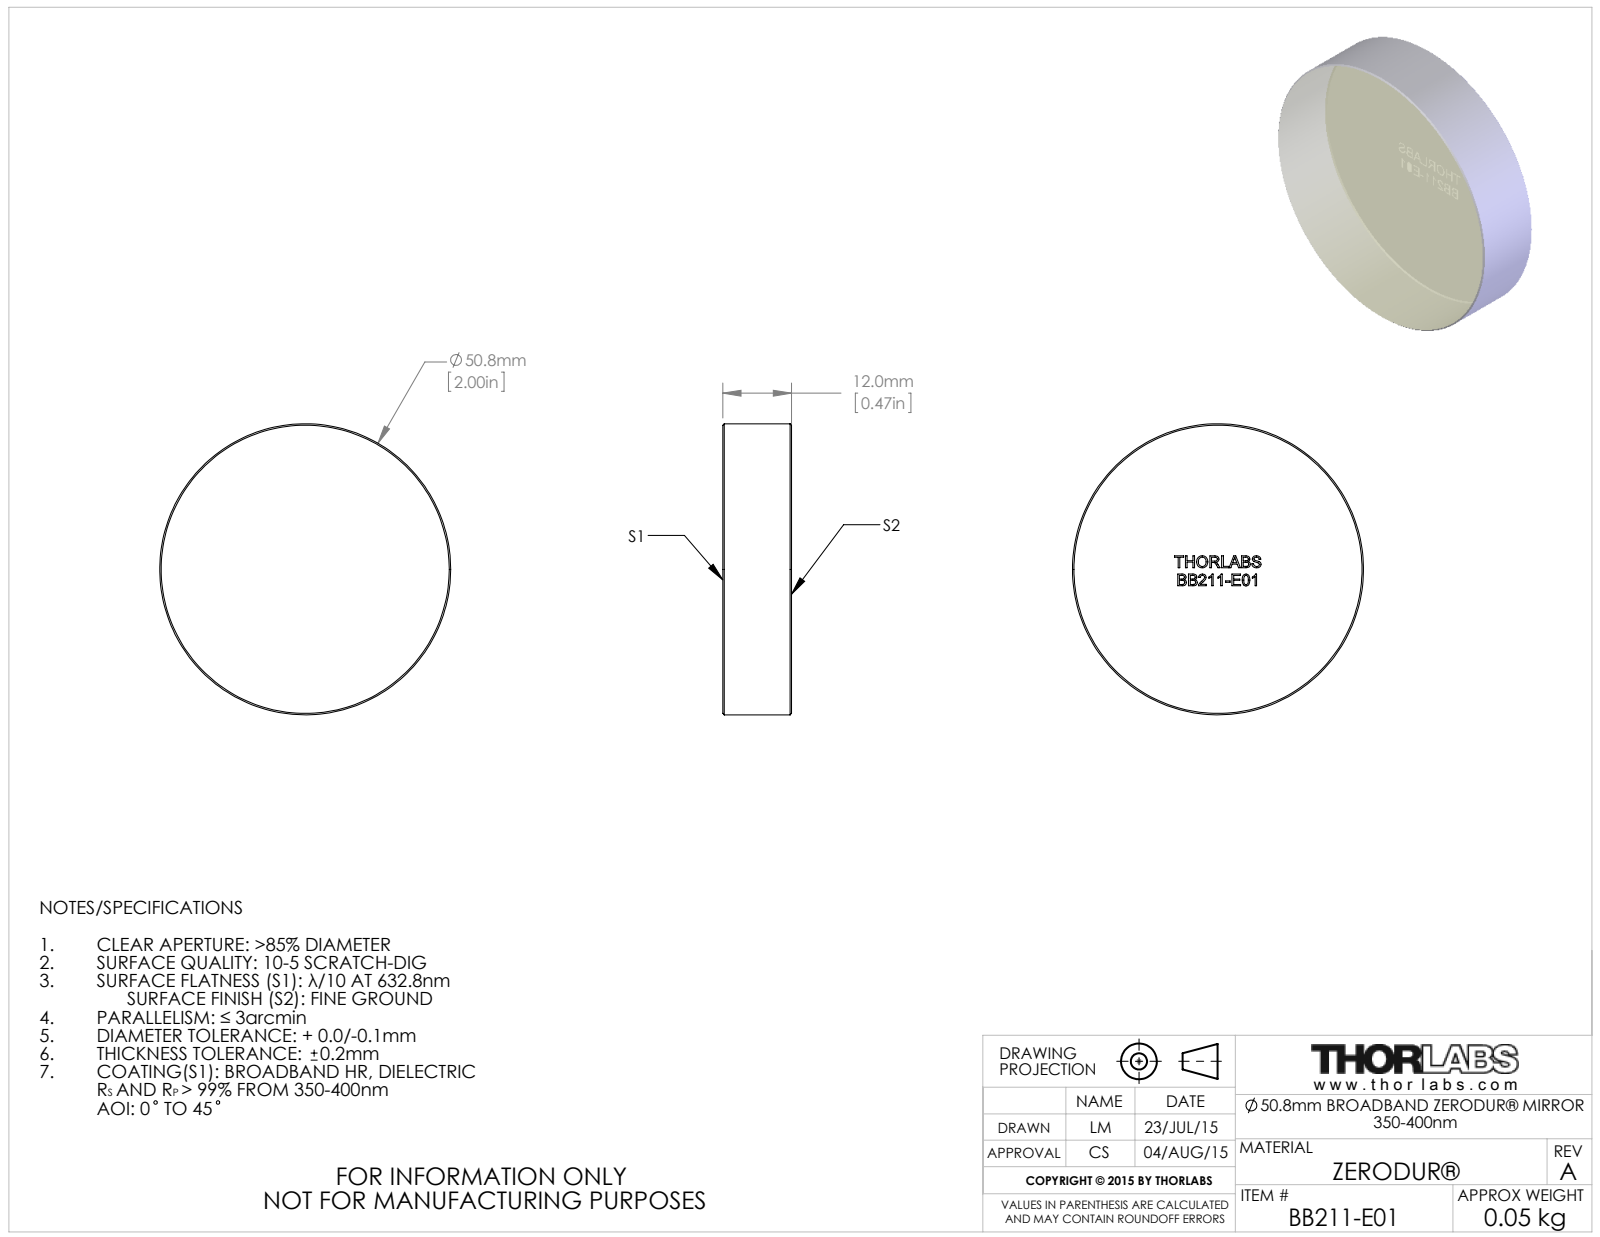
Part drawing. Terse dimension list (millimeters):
name: TTN045204-E0W
written by: SolidWorks 2014 (CONFIG_CONTROL_DESIGN)
unit: mm
bodies: 1 solid, 234 faces (141 planar, 2 cylindrical, 91 other)
size: 50.8 × 50.8 × 12
volume: 24 312 mm³; area: 5 922 mm²
bosses: 1× ⌀50.8
face distances: 12, 3.16, 1.58, 2.05, 4.03, 7.59, 5.53, 0.87, 2.93, 2.55
